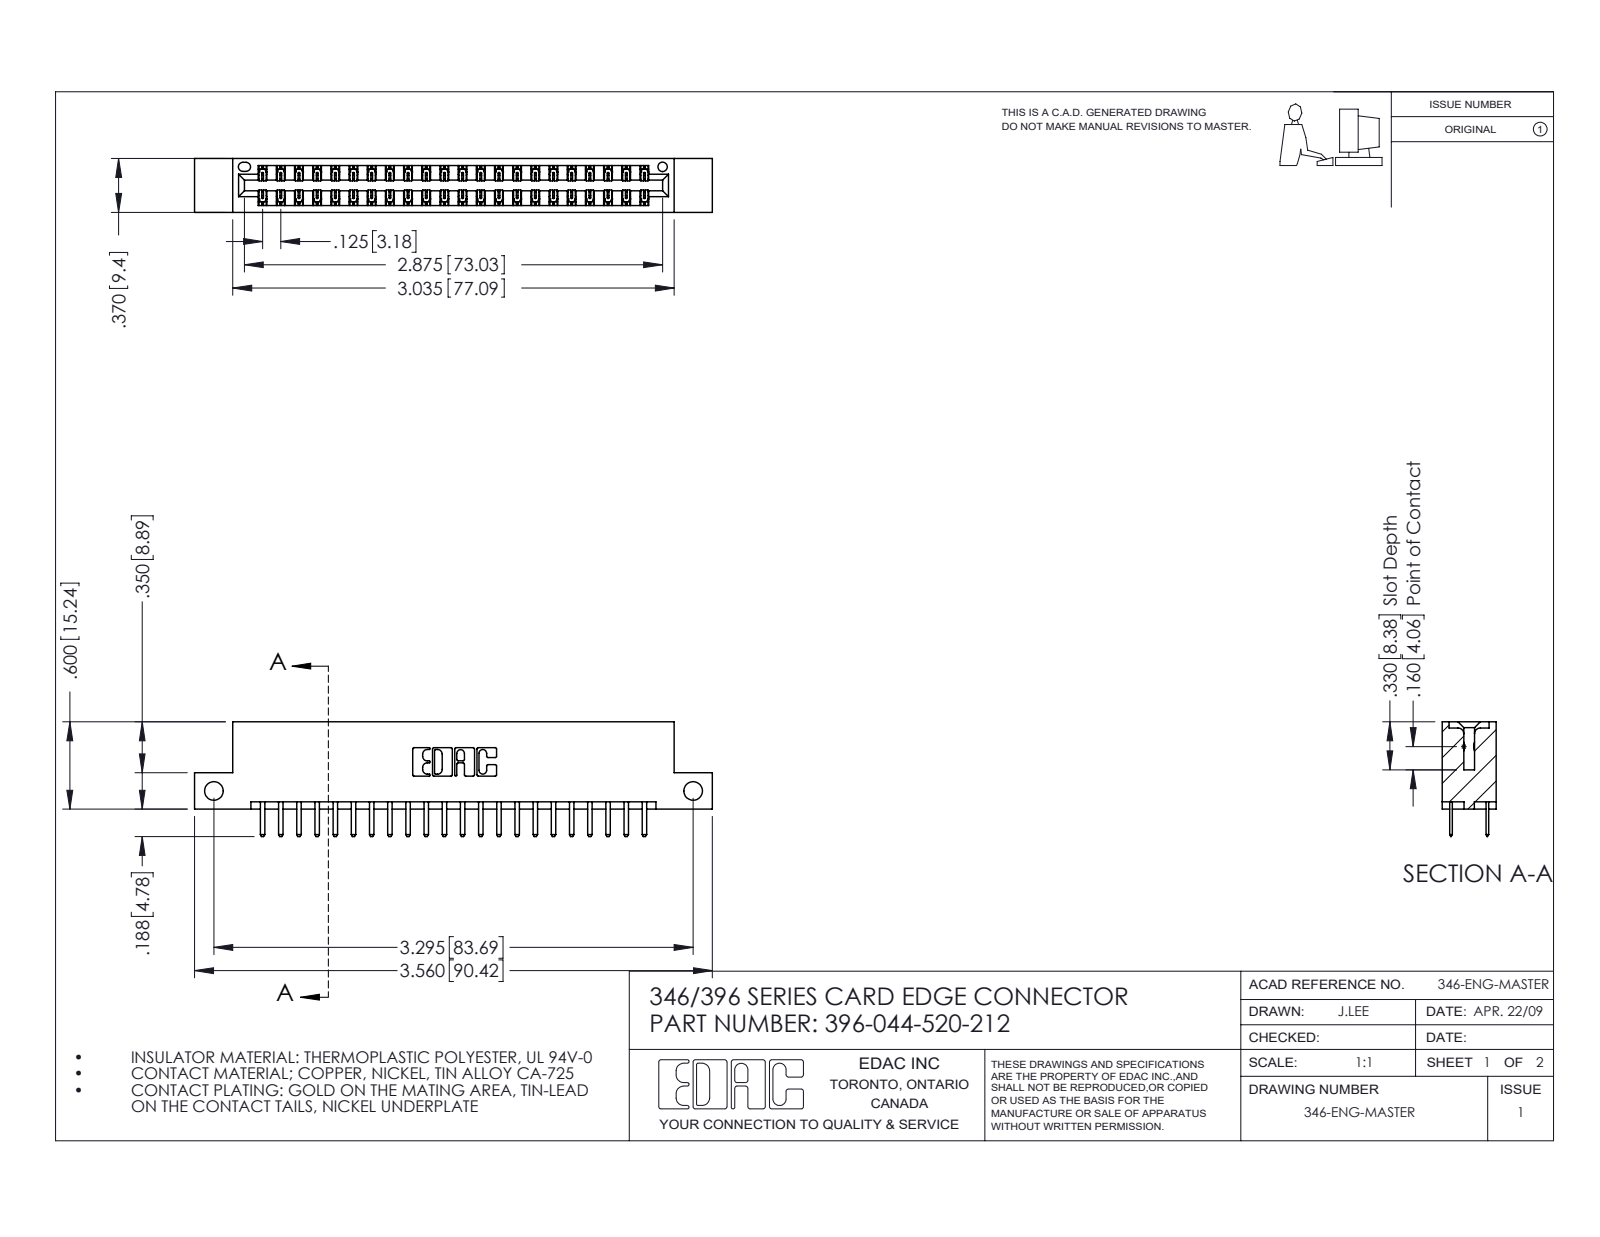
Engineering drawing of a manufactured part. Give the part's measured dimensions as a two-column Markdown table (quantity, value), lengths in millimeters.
| quantity | value |
| --- | --- |
| part name | 396-044-520-212; 345-292-001_345-293-120; 346 Part_Flush Mounting Lugs - Side Mount |
| STEP written by | SolidWorks 2016 (CONFIG_CONTROL_DESIGN) |
| units | millimeters |
| bodies | 45 solids, 2586 faces (1704 planar, 882 cylindrical, 0 other) |
| overall size | 90.4 × 20 × 9.4 |
| volume | 8 550 mm³ |
| surface area | 11 260 mm² |
| round holes (diameter × count) | 3.3 × 2, 1.6 × 1 |
| partial cylindrical surfaces (radius × count) | 0.2 × 66, 0.3 × 48, 0.3 × 22, 0.2 × 6, 0.8 × 6, 0.7 × 3, 0.4 × 2, 0.6 × 2 |
| main face-to-face distances | 1.2, 8.2, 6.4, 9.4, 7, 1.8, 7.6, 0.6, 3.8, 5.6 |
| hole center spacings | 83.7 |
